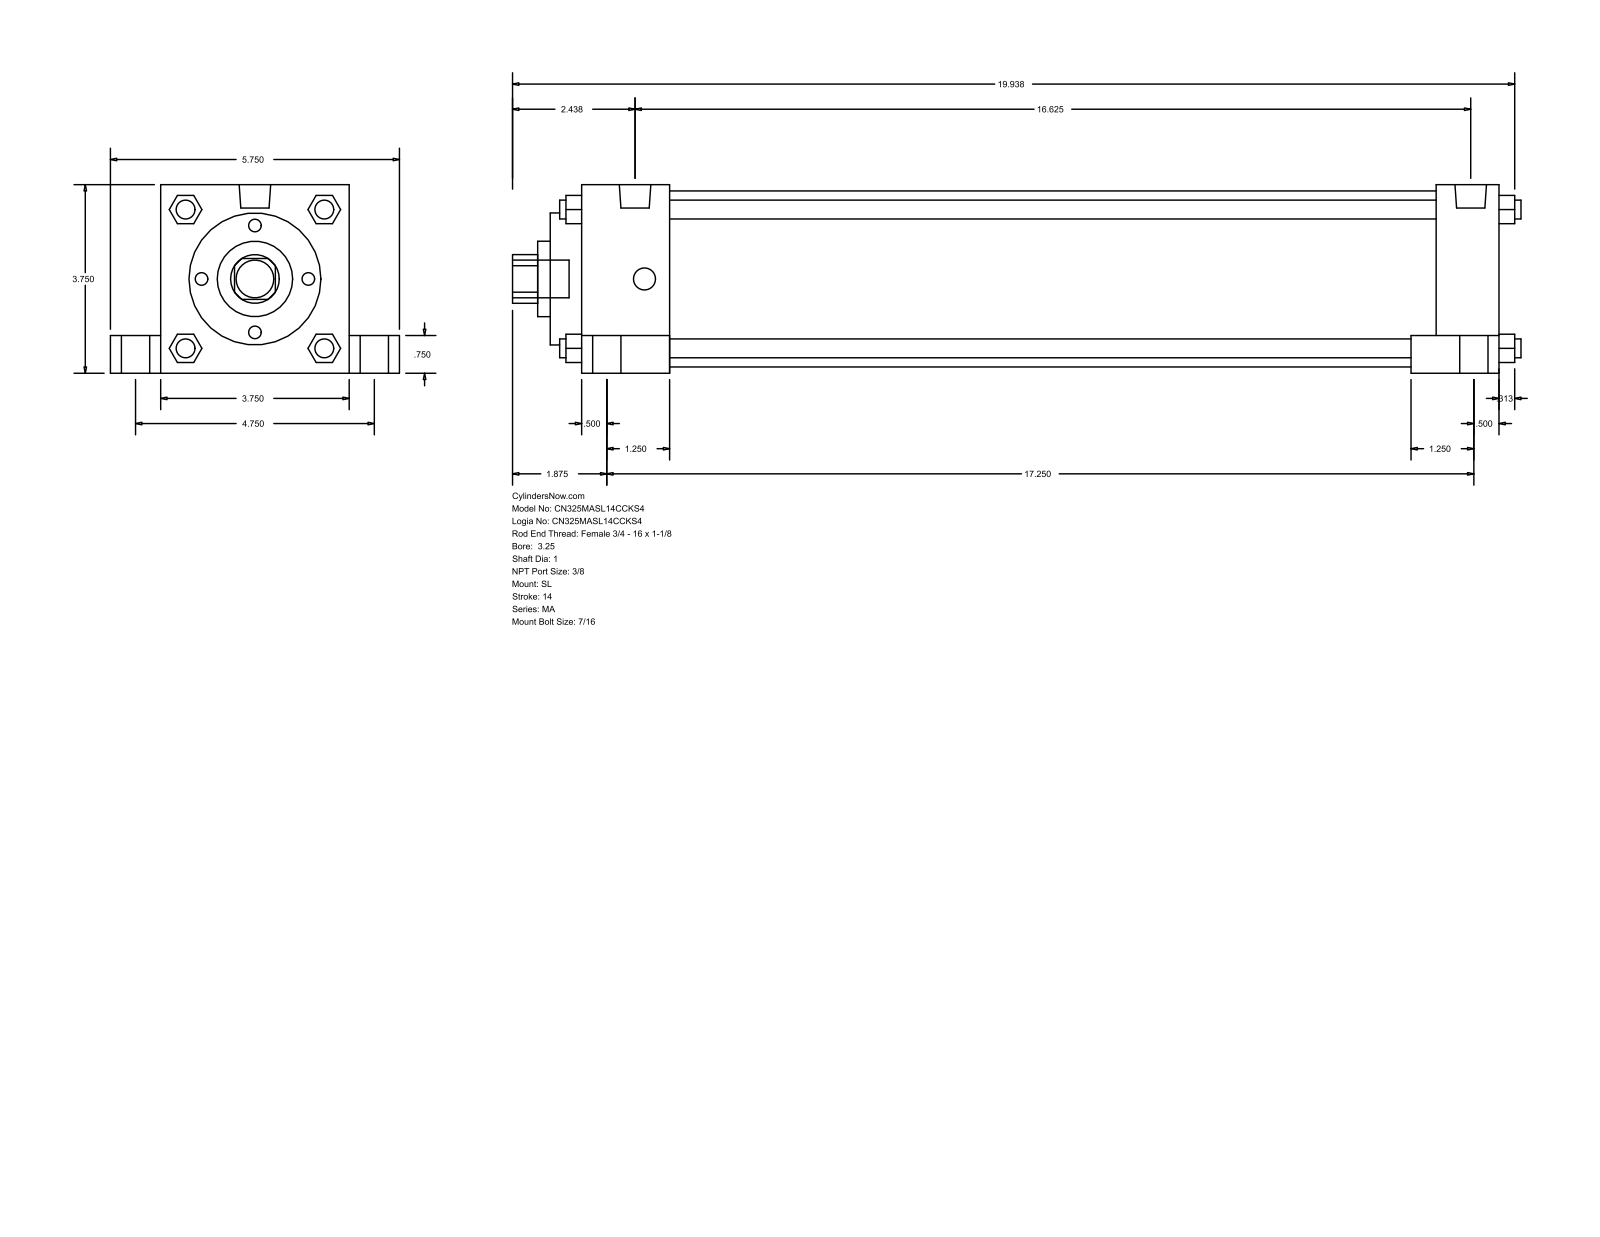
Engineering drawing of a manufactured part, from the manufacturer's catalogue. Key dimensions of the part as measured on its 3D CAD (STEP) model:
Part name (STEP PRODUCT): MA_SL__0325_1
STEP written by: GSSL Pune (CONFIG_CONTROL_DESIGN)
Units: millimetres
Bodies: 0 solids, 150 faces (113 planar, 37 cylindrical, 0 other)
Overall size (bounding box): 509.59 × 146.05 × 95.25
Round holes (diameter × count): ⌀25.4 ×1, ⌀38.1 ×1, ⌀66.67 ×1, ⌀88.9 ×1
Round bosses / shafts (diameter × count): ⌀20.64 ×4, ⌀14.29 ×4, ⌀11.11 ×4, ⌀9.53 ×4, ⌀15.93 ×2, ⌀19.05 ×1
Partial cylindrical surfaces — rounded edges, fillets, slot ends (radius × count): R12.29 ×1
Main face-to-face distances: 95.24, 463.56, 387.35, 15.87, 25.41, 120.65, 19.05, 431.81, 31.75, 44.46
